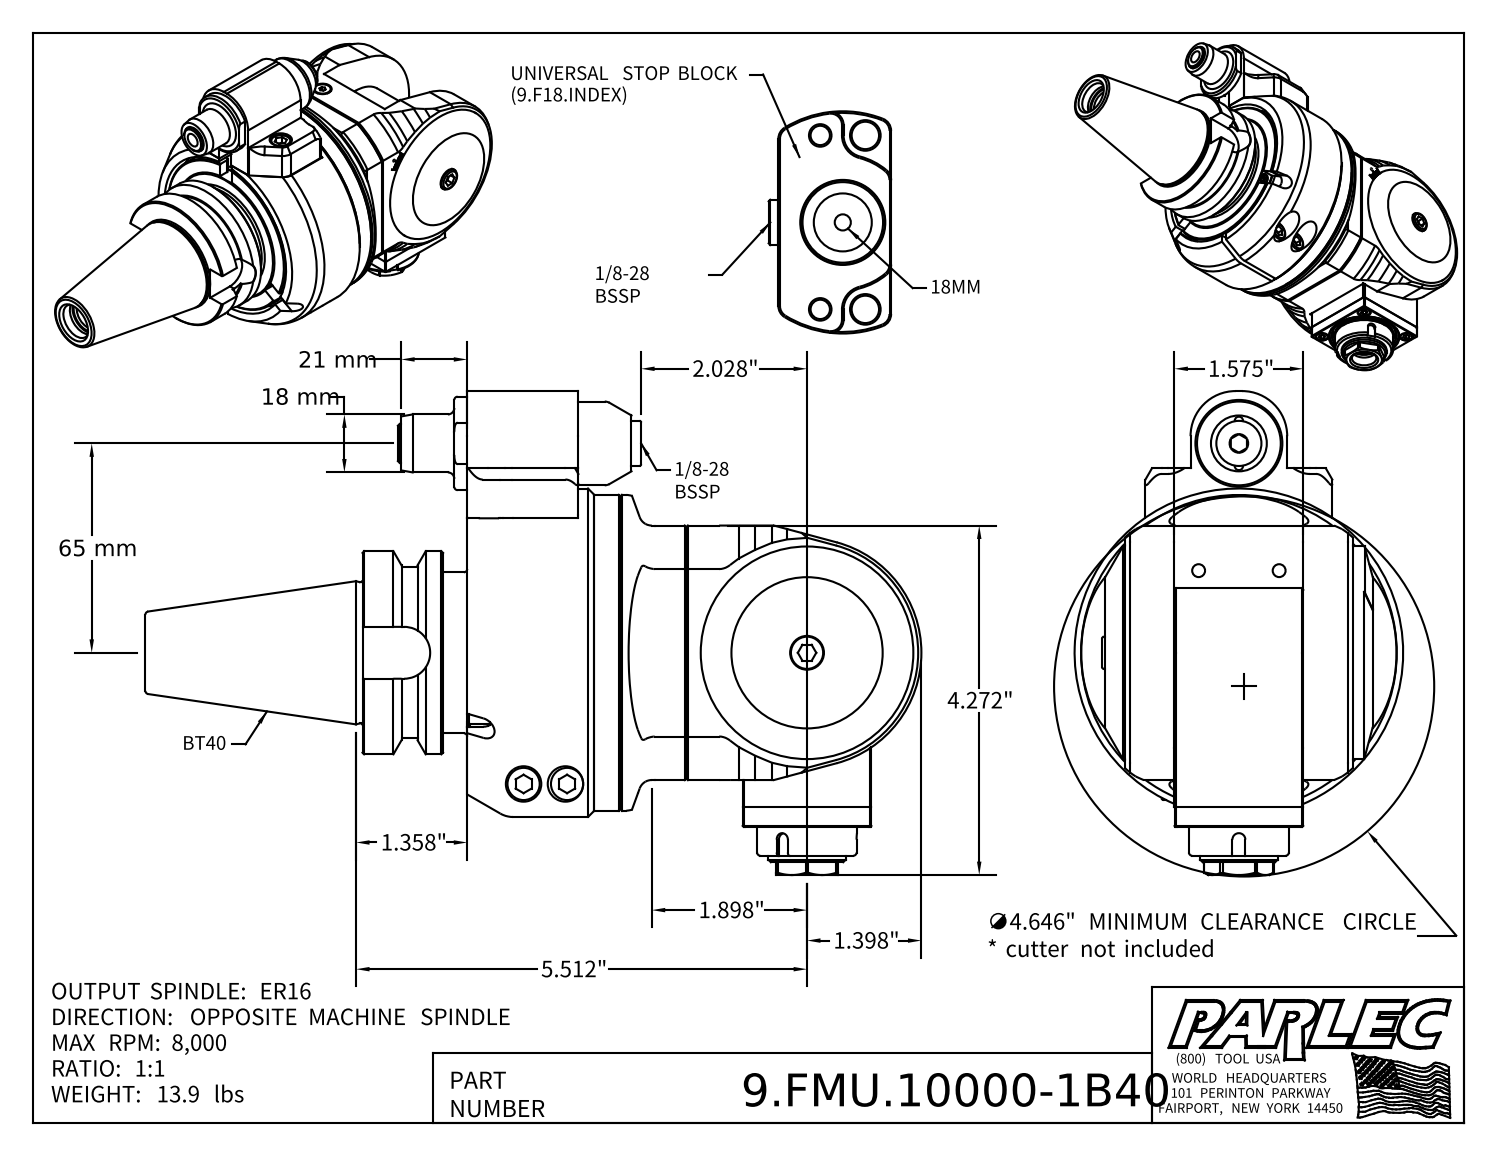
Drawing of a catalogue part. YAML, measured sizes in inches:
part_name: "9.FMU.10000-1B40; 9_FMU_10000; 9_GA1_346_2 (Type 1, BT40, 65mm)"
step_written_by: "Autodesk Inventor 2022 (AUTOMOTIVE_DESIGN)"
units: inches
bodies: {solids: 6, faces: 681, planar: 344, cylindrical: 151, other: 186}
overall_size: [9.484, 5.915, 4.016]
volume: 62.83
surface_area: 268.7
round_holes:
  - {diameter: 0.276, count: 5}
  - {diameter: 0.413, count: 3}
  - {diameter: 0.433, count: 3}
  - {diameter: 0.102, count: 2}
  - {diameter: 0.157, count: 2}
  - {diameter: 0.165, count: 2}
  - {diameter: 0.197, count: 2}
  - {diameter: 0.335, count: 2}
  - {diameter: 0.409, count: 2}
  - {diameter: 0.512, count: 2}
  - {diameter: 0.098, count: 1}
  - {diameter: 0.118, count: 1}
round_bosses_or_shafts:
  - {diameter: 0.394, count: 7}
  - {diameter: 0.236, count: 4}
  - {diameter: 0.315, count: 3}
  - {diameter: 0.709, count: 2}
  - {diameter: 0.098, count: 2}
  - {diameter: 4.016, count: 1}
  - {diameter: 3.858, count: 1}
  - {diameter: 3.031, count: 1}
partial_cylinders:
  - {radius: 0.079, count: 11}
  - {radius: 0.157, count: 6}
  - {radius: 0.02, count: 2}
  - {radius: 0.039, count: 2}
  - {radius: 0.138, count: 2}
  - {radius: 0.197, count: 2}
  - {radius: 0.551, count: 2}
  - {radius: 0.317, count: 1}
face_to_face_distances: [0.531, 2.106, 1.575, 1.26, 0.61, 0.315, 2.185, 2.717, 0.079, 2.638]
hole_center_spacings: [0.886, 1.253, 0.276, 0.394, 0.872, 0.9, 1.118, 1.371]
